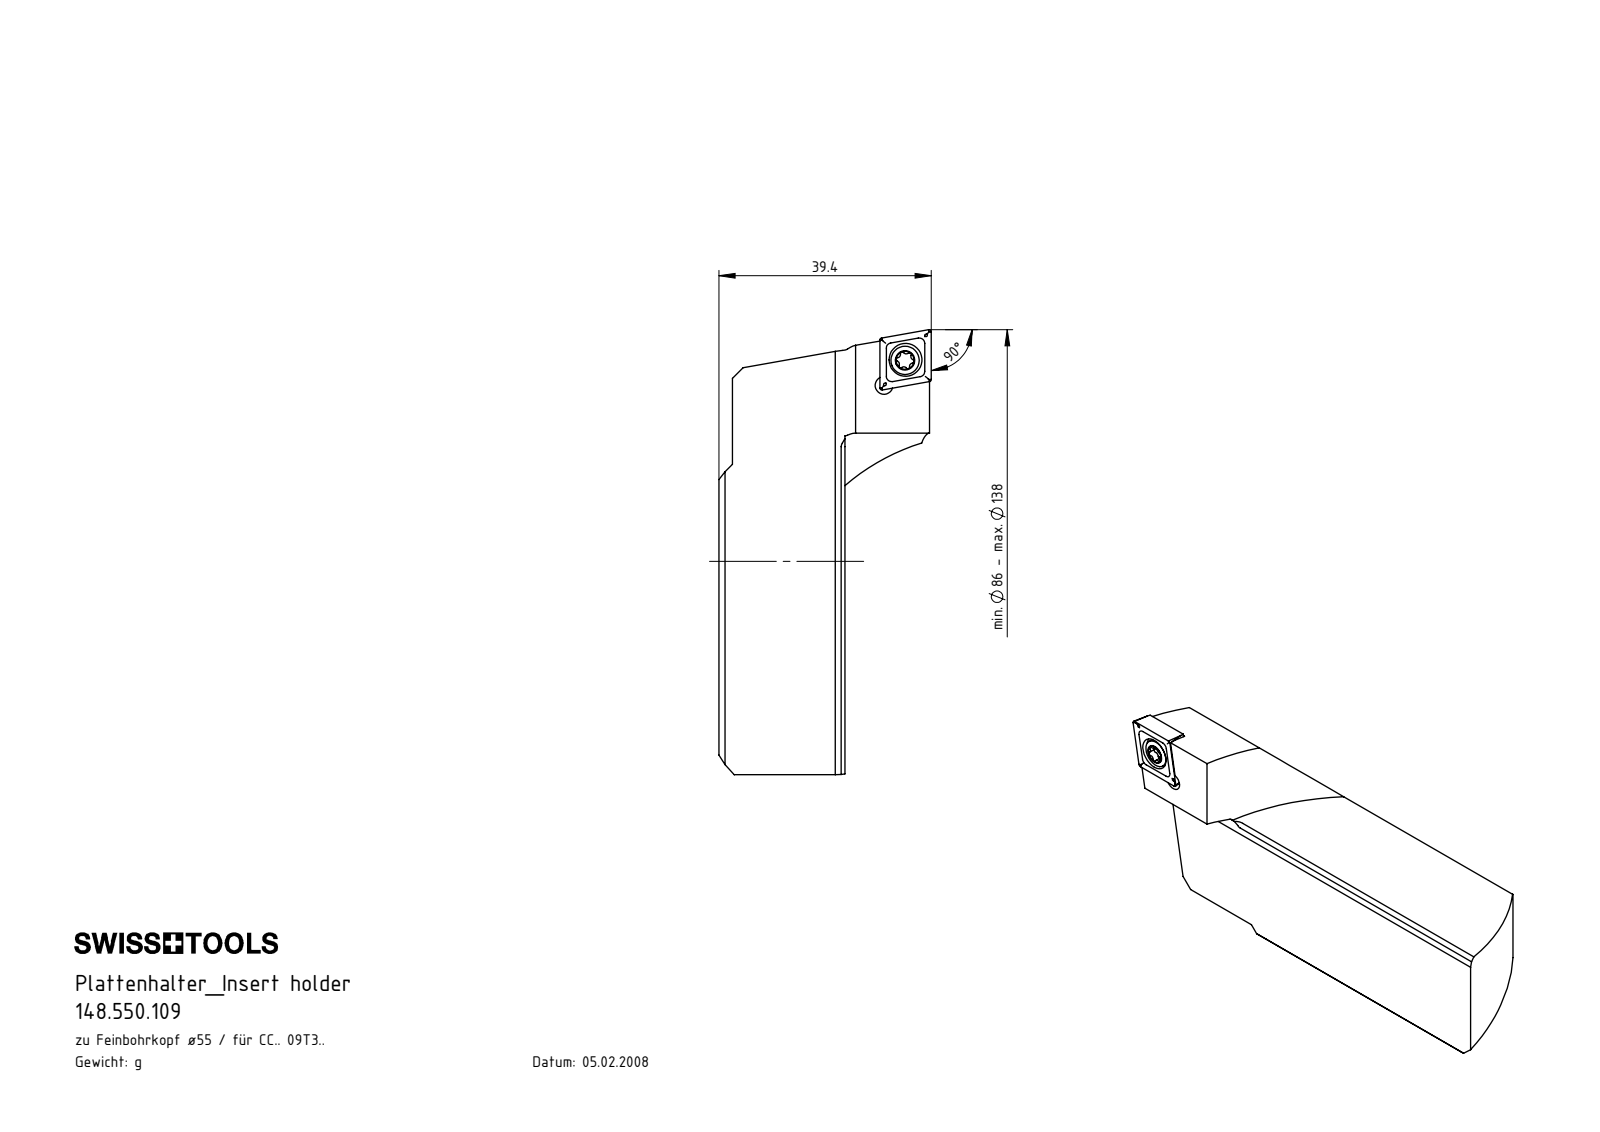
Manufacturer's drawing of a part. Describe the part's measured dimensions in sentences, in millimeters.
The part is named "F00-WCB.086.001_C; CCMT09T304; WCB-ER2.001.009_A; 148.550.109". Its 3-D file was written by "SolidWorks 2017 (CONFIG_CONTROL_DESIGN)". It is 3 solids with 382 faces: 226 planar, 39 cylindrical and 117 other. Overall it measures 82.57 by 39.4 by 27.35 millimeters. Its volume is 33 561 cubic millimeters and its surface area 8 976 square millimeters. Round holes: 2 of diameter 3.3, 1 of diameter 4.4, 1 of diameter 6.1. Round bosses or shafts: 1 of diameter 5.25, 1 of diameter 4. Partial cylindrical surfaces (rounded edges, fillets, slot ends): 8 of radius 0.2, 6 of radius 0.34, 6 of radius 0.59, 3 of radius 40, 1 of radius 0.8. The main face-to-face distances are 2.38, 4.76, 21.3, 7.14, 9.52, 4.77, 7.15, 9.53, 11.91, 11.9. The hole center spacings are 6.07, 6.19.
